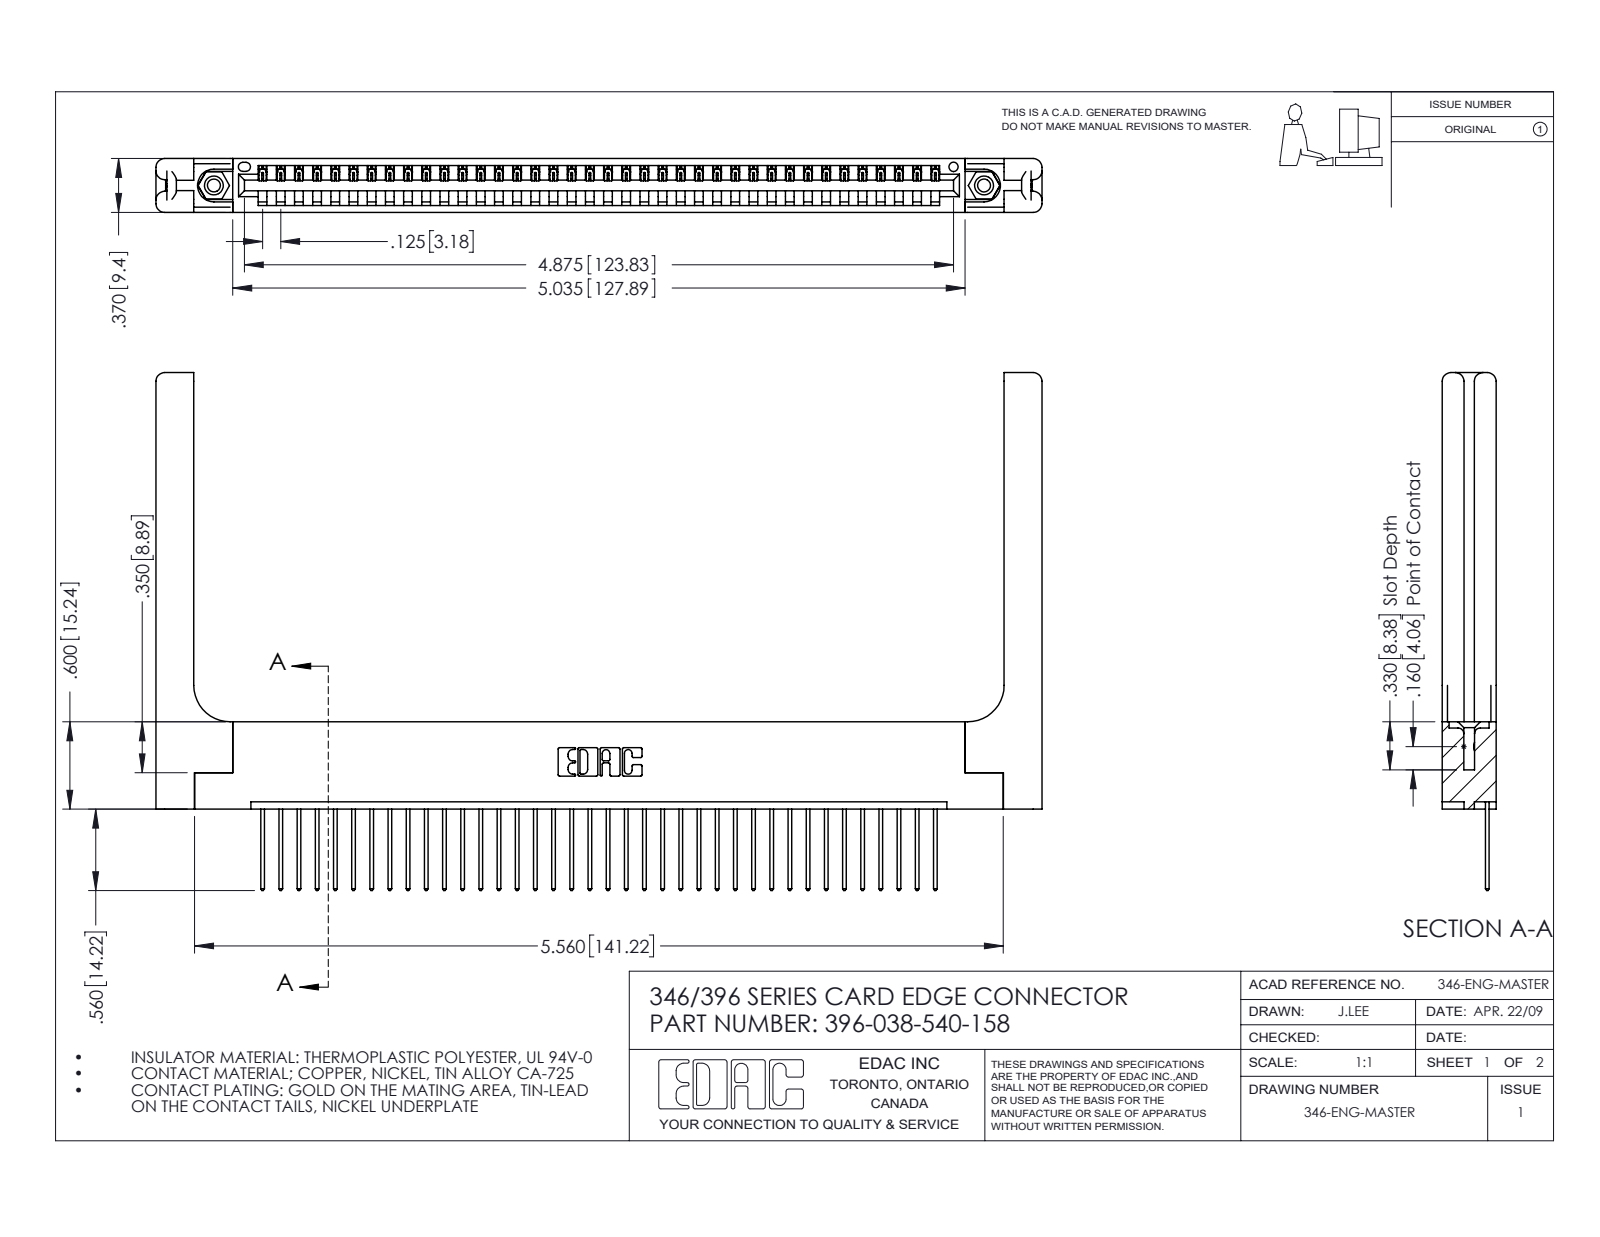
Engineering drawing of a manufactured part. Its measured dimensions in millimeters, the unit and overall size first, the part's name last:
Units: millimetres
Overall size (bounding box): 154.7 × 90.4 × 9.4
Round holes (diameter × count): ⌀2.3 ×2, ⌀3.2 ×2, ⌀4 ×2, ⌀1.6 ×1
Round bosses / shafts (diameter × count): ⌀3.9 ×2
Partial cylindrical surfaces — rounded edges, fillets, slot ends (radius × count): R0.2 ×76, R0.3 ×76, R0.3 ×22, R1.5 ×16, R0.2 ×6, R0.8 ×6, R0.7 ×3, R0.8 ×2
Main face-to-face distances: 9.4, 1.2, 8.2, 1.8, 3.8, 3.8, 6.4, 7.6, 0.6, 5.6
Hole centre spacings: 6.2, 129.2, 134.5
Volume: 22 350 mm³ · Surface area: 24 040 mm²
Bodies: 43 solids, 2582 faces (1744 planar, 778 cylindrical, 60 other)
Part name (STEP PRODUCT): 345-250-001_345-250-001-102; 345-292-001_345-293-140; 346 Part_Flush Mounting Lugs - 0.156 Dia-TH; 346-220-058_345-220-058 (+1 more)
STEP written by: SolidWorks 2016 (CONFIG_CONTROL_DESIGN)
